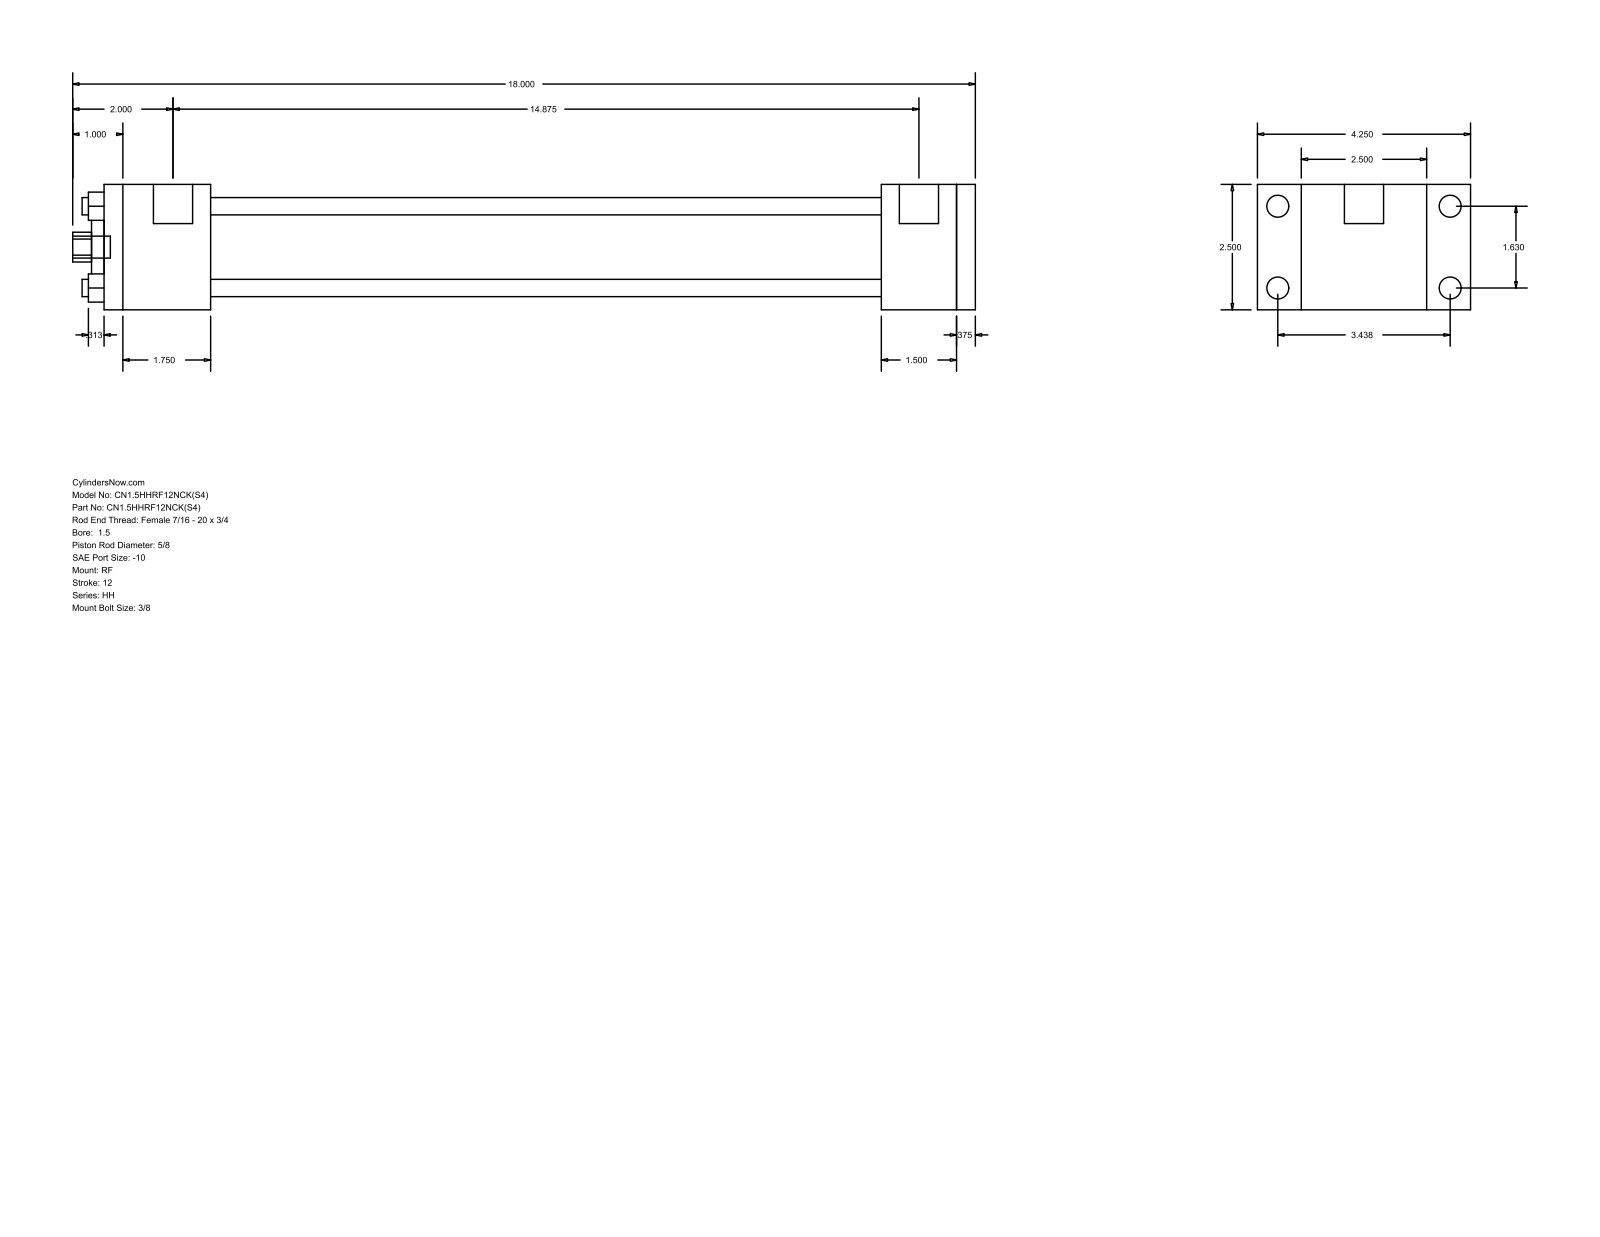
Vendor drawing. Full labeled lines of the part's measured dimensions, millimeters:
Part name (STEP PRODUCT): HH_RF__0150_0.625
STEP written by: GSSL Pune (CONFIG_CONTROL_DESIGN)
Units: millimetres
Bodies: 0 solids, 92 faces (64 planar, 28 cylindrical, 0 other)
Overall size (bounding box): 457.2 × 107.95 × 63.5
Round holes (diameter × count): ⌀8.76 ×4, ⌀15.88 ×1, ⌀28.57 ×1, ⌀44.45 ×1
Round bosses / shafts (diameter × count): ⌀11.13 ×4, ⌀5.56 ×4, ⌀19.84 ×2, ⌀11.11 ×1
Partial cylindrical surfaces — rounded edges, fillets, slot ends (radius × count): R7.54 ×1
Main face-to-face distances: 63.5, 441.32, 9.52, 431.8, 47.63, 53.97, 393.69, 339.72, 377.83, 387.35
Hole centre spacings: 29.27, 41.4, 58.55
